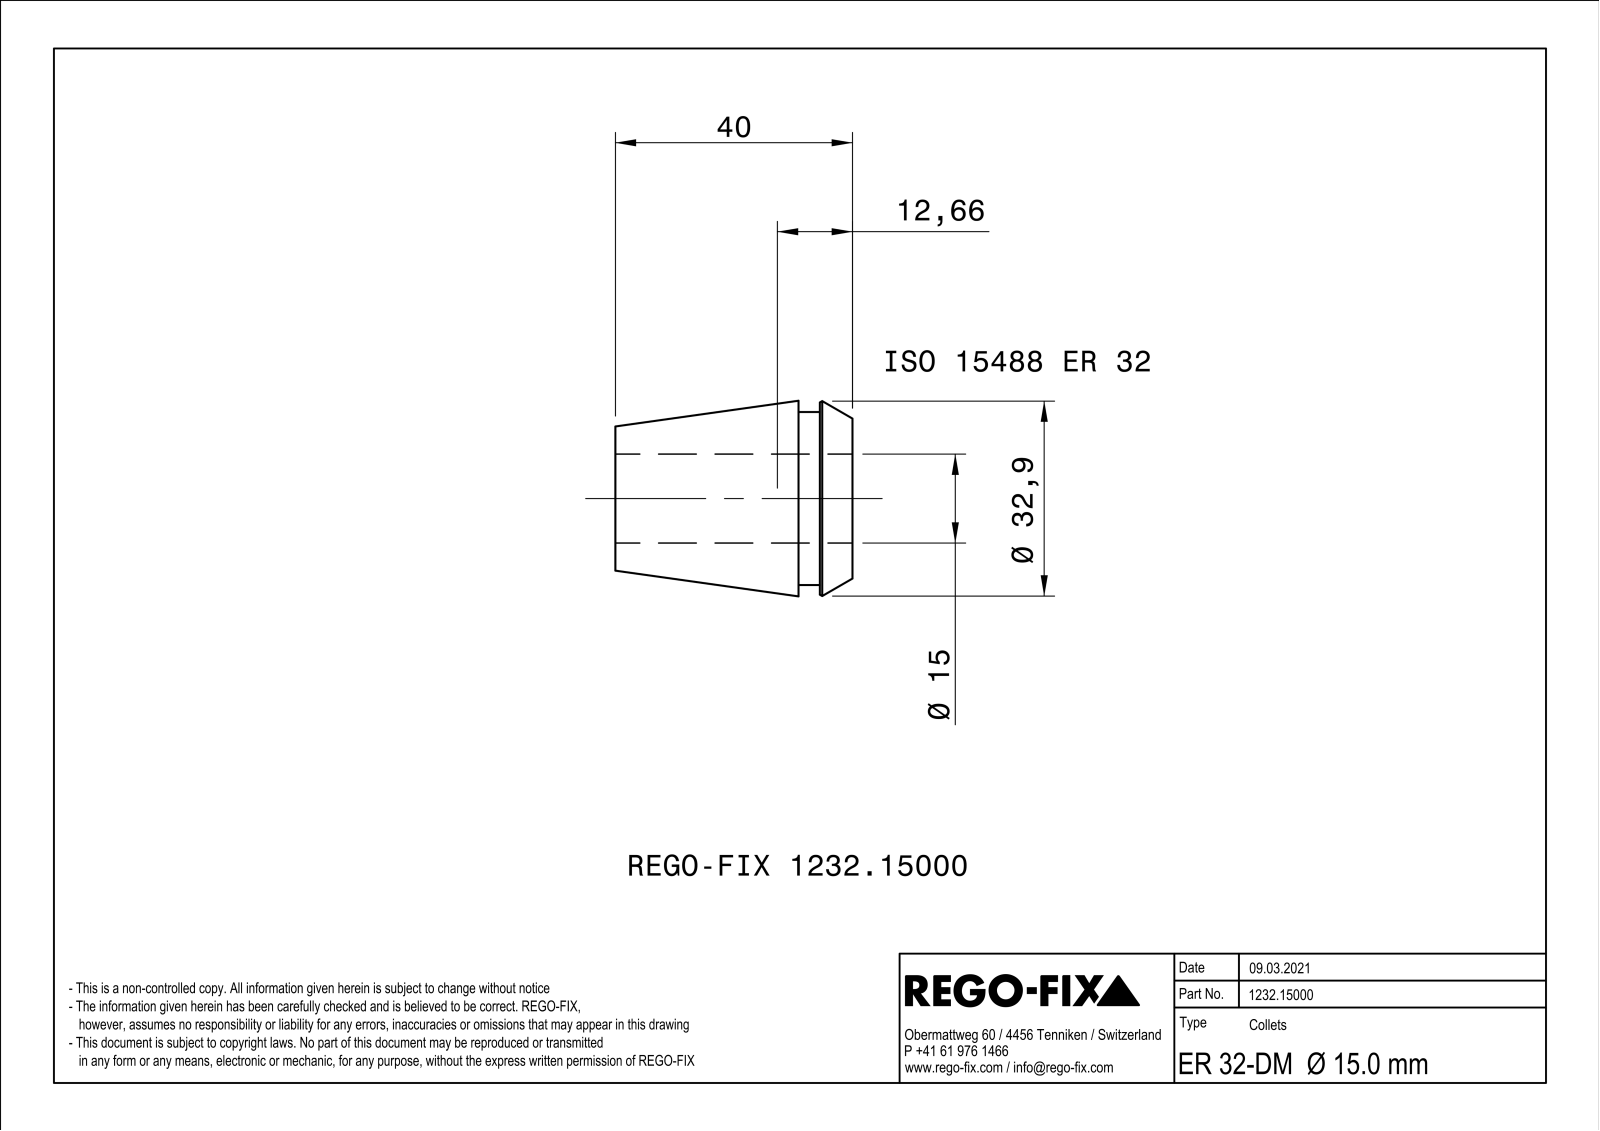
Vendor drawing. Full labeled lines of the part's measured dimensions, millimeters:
Part name (STEP PRODUCT): NOCUT
STEP written by: SIEMENS PLM Software Solid Edge ST10 (AUTOMOTIVE_DESIGN)
Units: millimetres
Bodies: 1 solid, 154 faces (80 planar, 9 cylindrical, 65 other)
Overall size (bounding box): 40 × 32.98 × 32.98
Volume: 16 117 mm³ · Surface area: 12 154 mm²
Round holes (diameter × count): ⌀15 ×1
Round bosses / shafts (diameter × count): ⌀29.2 ×1
Main face-to-face distances: 1, 40, 9.1, 30.9, 5.5, 3.6, 34.5, 16, 10.5, 6.9
